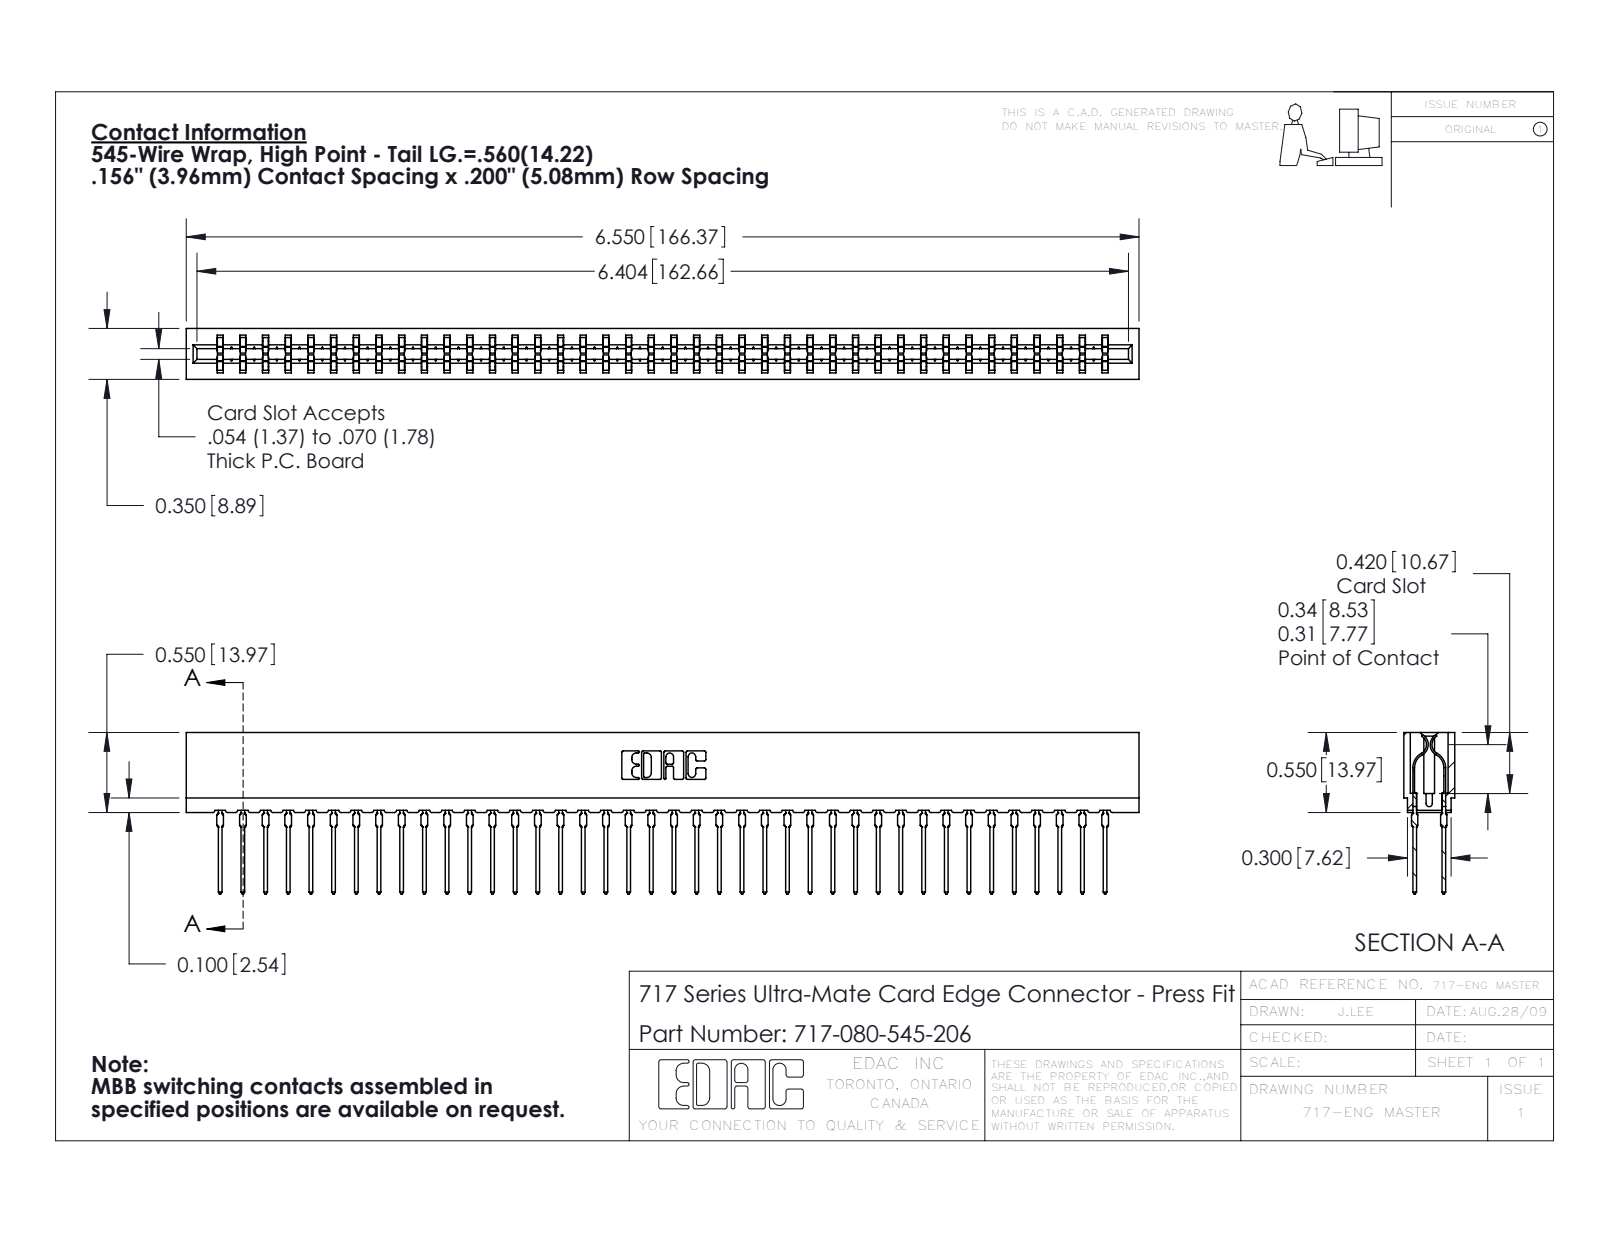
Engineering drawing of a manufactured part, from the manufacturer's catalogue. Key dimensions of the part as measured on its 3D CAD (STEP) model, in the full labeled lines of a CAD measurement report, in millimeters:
Part name (STEP PRODUCT): 745-292-001_545; 717 Part_Insulator Option - 06; 717-080-545-206
STEP written by: SolidWorks 2016 (CONFIG_CONTROL_DESIGN)
Units: millimetres
Bodies: 81 solids, 7294 faces (3774 planar, 1440 cylindrical, 2080 other)
Overall size (bounding box): 166.4 × 28.2 × 8.9
Volume: 14 700 mm³ · Surface area: 23 830 mm²
Partial cylindrical surfaces — rounded edges, fillets, slot ends (radius × count): R0.5 ×160, R0.4 ×80, R0.3 ×22, R0.1 ×8, R0.3 ×8, R0.2 ×6, R0.8 ×6, R0.7 ×3
Main face-to-face distances: 5.4, 3.5, 8.9, 1.6, 7.3, 1.9, 3.8, 1.9, 2.2, 6.7
